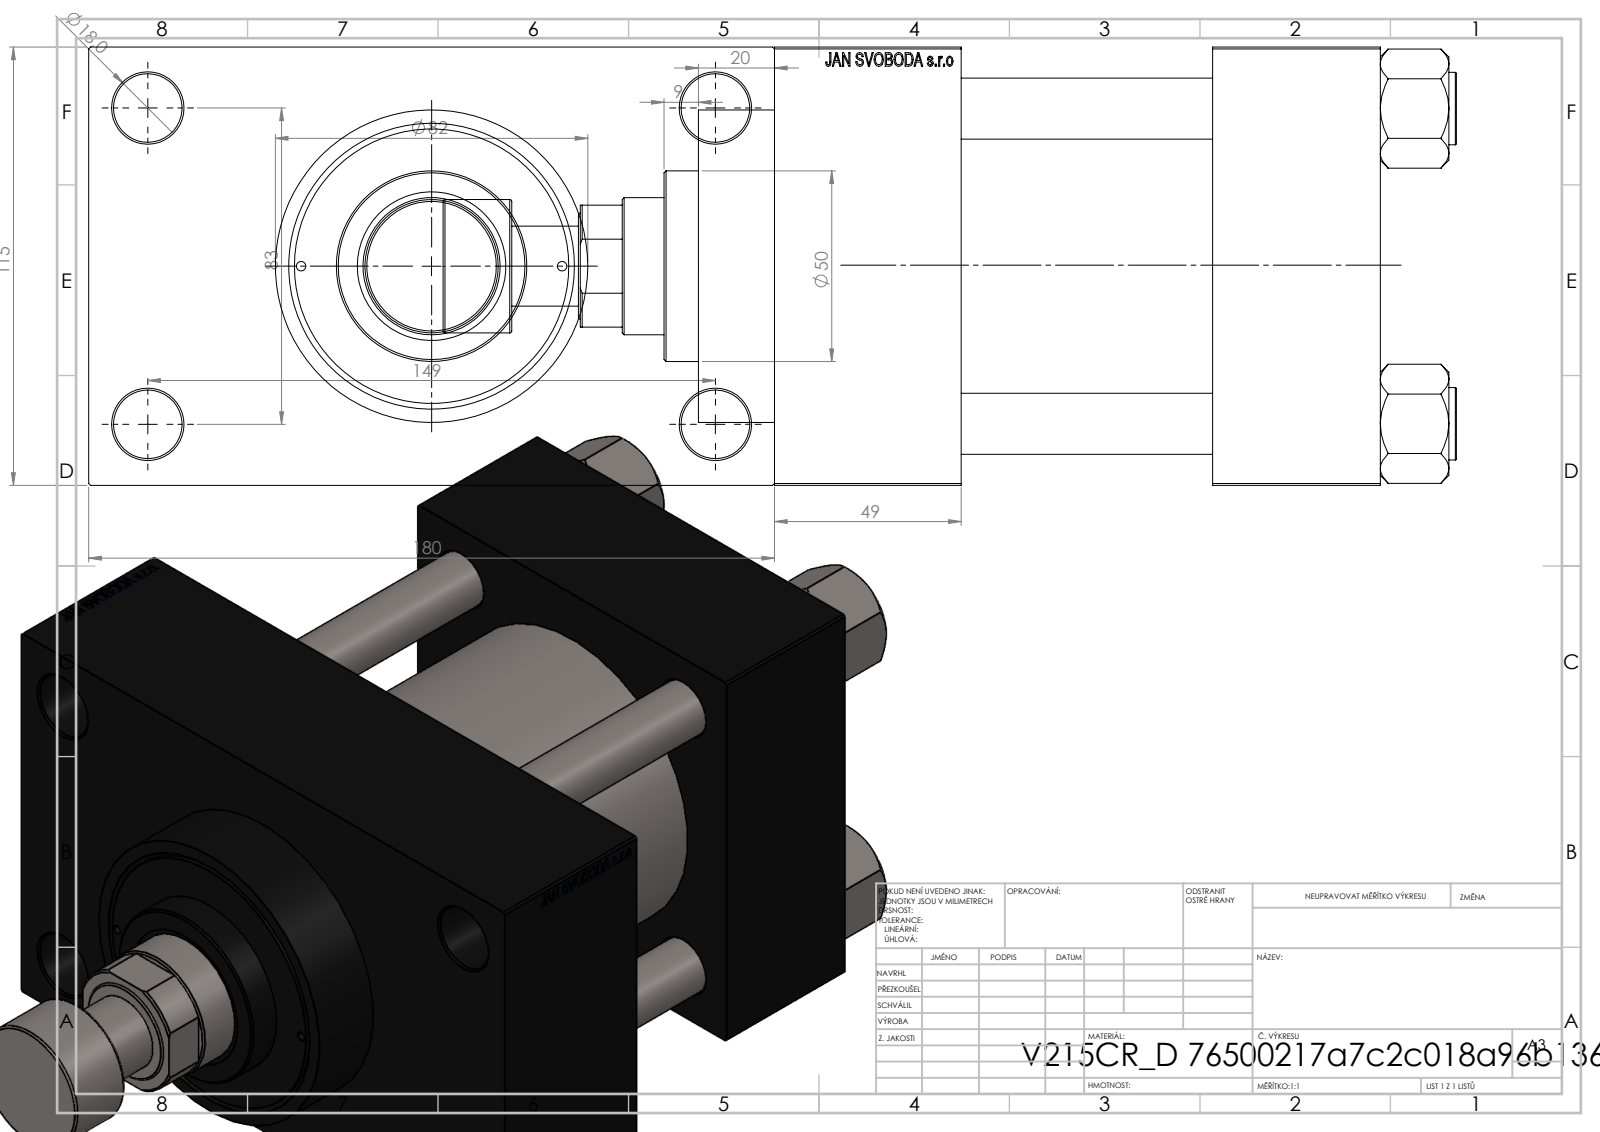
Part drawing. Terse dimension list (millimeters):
name: V215_VC_A; V215CR_ROD_END_F; V215CR_D_Body; V215CR_D_TYCINKA (+2 more)
written by: SolidWorks 2019 (CONFIG_CONTROL_DESIGN)
unit: mm
bodies: 12 solids, 1173 faces (551 planar, 96 cylindrical, 526 other)
size: 266 × 180 × 115
volume: 2 003 000 mm³; area: 302 044 mm²
holes: 4× ⌀16, 4× ⌀18, 2× ⌀2.5, 2× ⌀7, 2× ⌀26.44, 2× ⌀35, 1× ⌀25.5, 1× ⌀36, 1× ⌀39, 1× ⌀61, 1× ⌀72, 1× ⌀80
bosses: 4× ⌀19, 1× ⌀86, 1× ⌀82, 1× ⌀50, 1× ⌀35, 1× ⌀21
face distances: 115, 66, 49, 110, 44, 159, 32.5, 147.5, 20, 69
hole spacings: 33.15, 41.96, 57.81, 58.48, 82.7, 85.28, 86.17, 89.24
